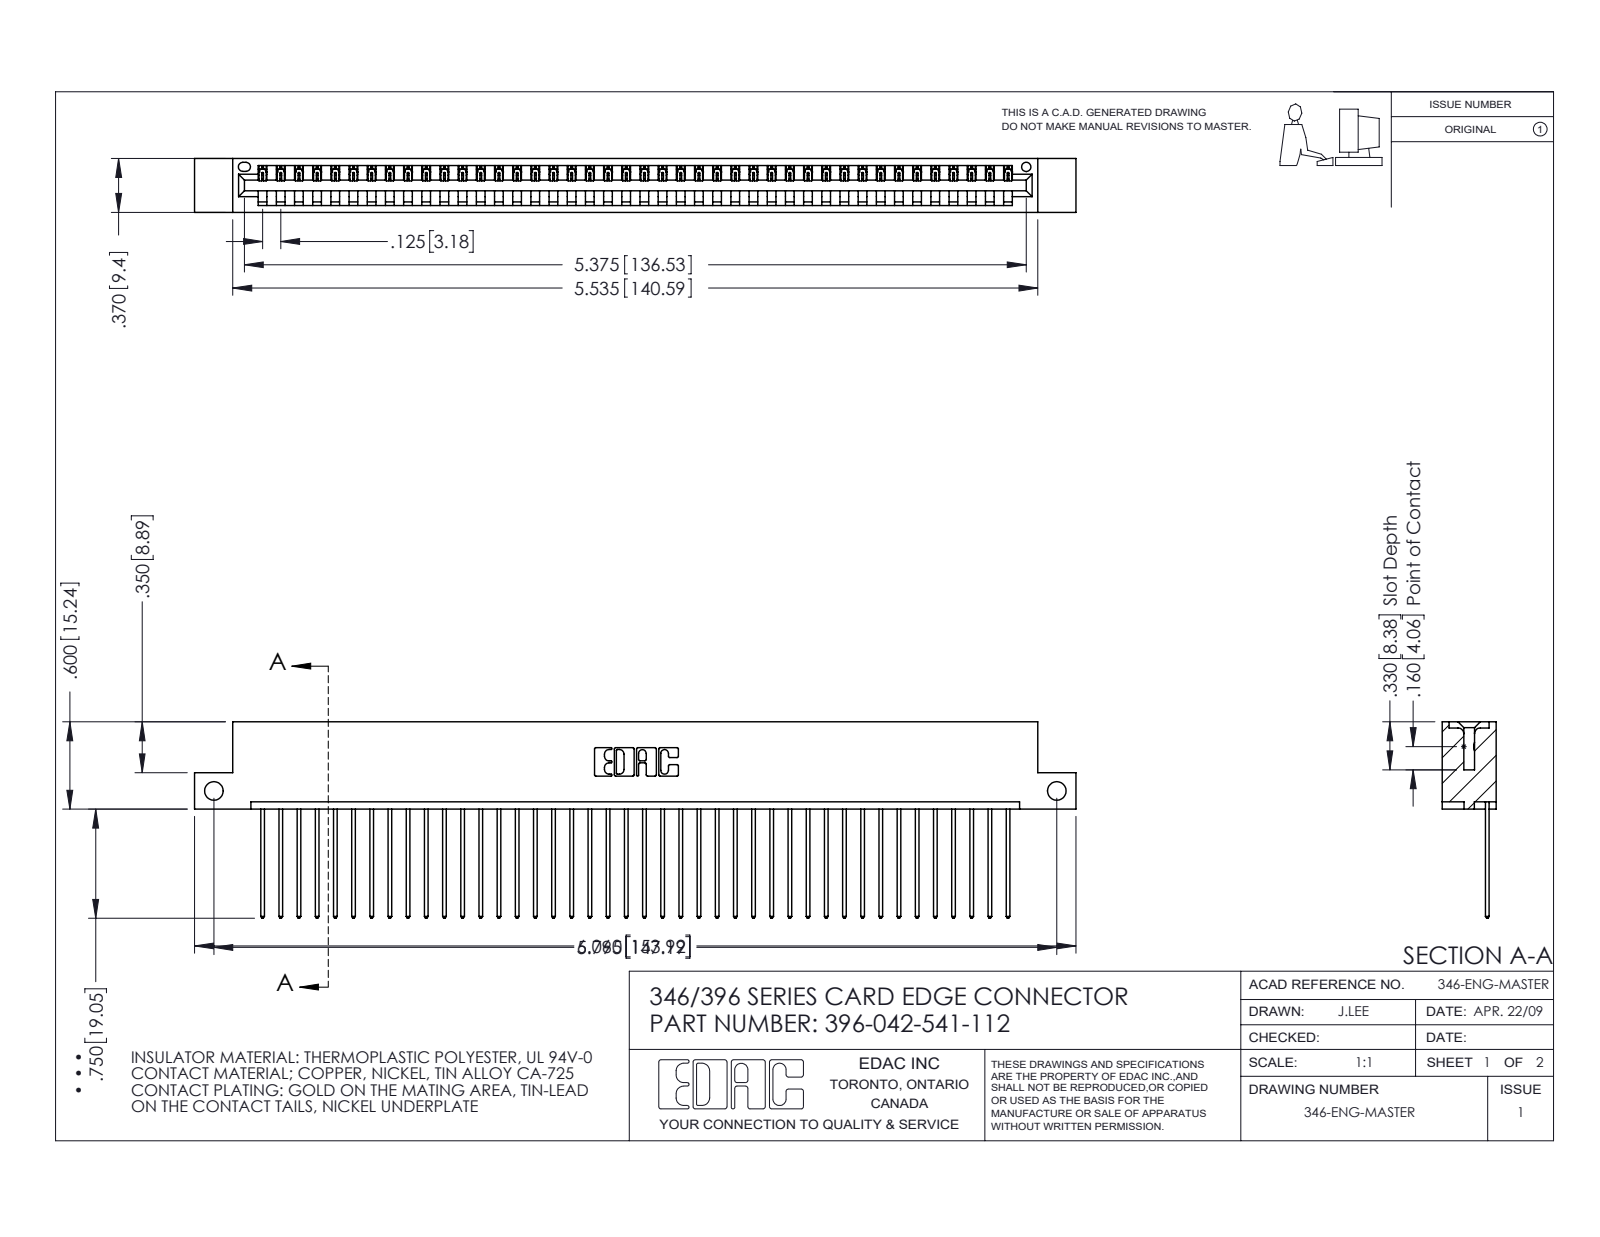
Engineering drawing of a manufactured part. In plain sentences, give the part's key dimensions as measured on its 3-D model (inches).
The part is named "345-292-001_345-293-141; 396-042-541-112; 346 Part_Flush Mounting Lugs - Side Mount". Its 3-D file was written by "SolidWorks 2016 (CONFIG_CONTROL_DESIGN)". It is 43 solids with 2558 faces: 1756 planar, 802 cylindrical and 0 other. Overall it measures 6.06 by 1.35 by 0.37 inches. Its volume is 0.902 cubic inches and its surface area 29.7 square inches. Round holes: 2 of diameter 0.128, 1 of diameter 0.064. Partial cylindrical surfaces (rounded edges, fillets, slot ends): 84 of radius 0.006, 84 of radius 0.01, 22 of radius 0.01, 6 of radius 0.007, 6 of radius 0.031, 3 of radius 0.026, 2 of radius 0.031, 2 of radius 0.04. The main face-to-face distances are 0.048, 0.322, 0.37, 0.25, 0.072, 0.298, 0.025, 0.148, 0.222, 0.1. The hole center spacings are 5.795.
